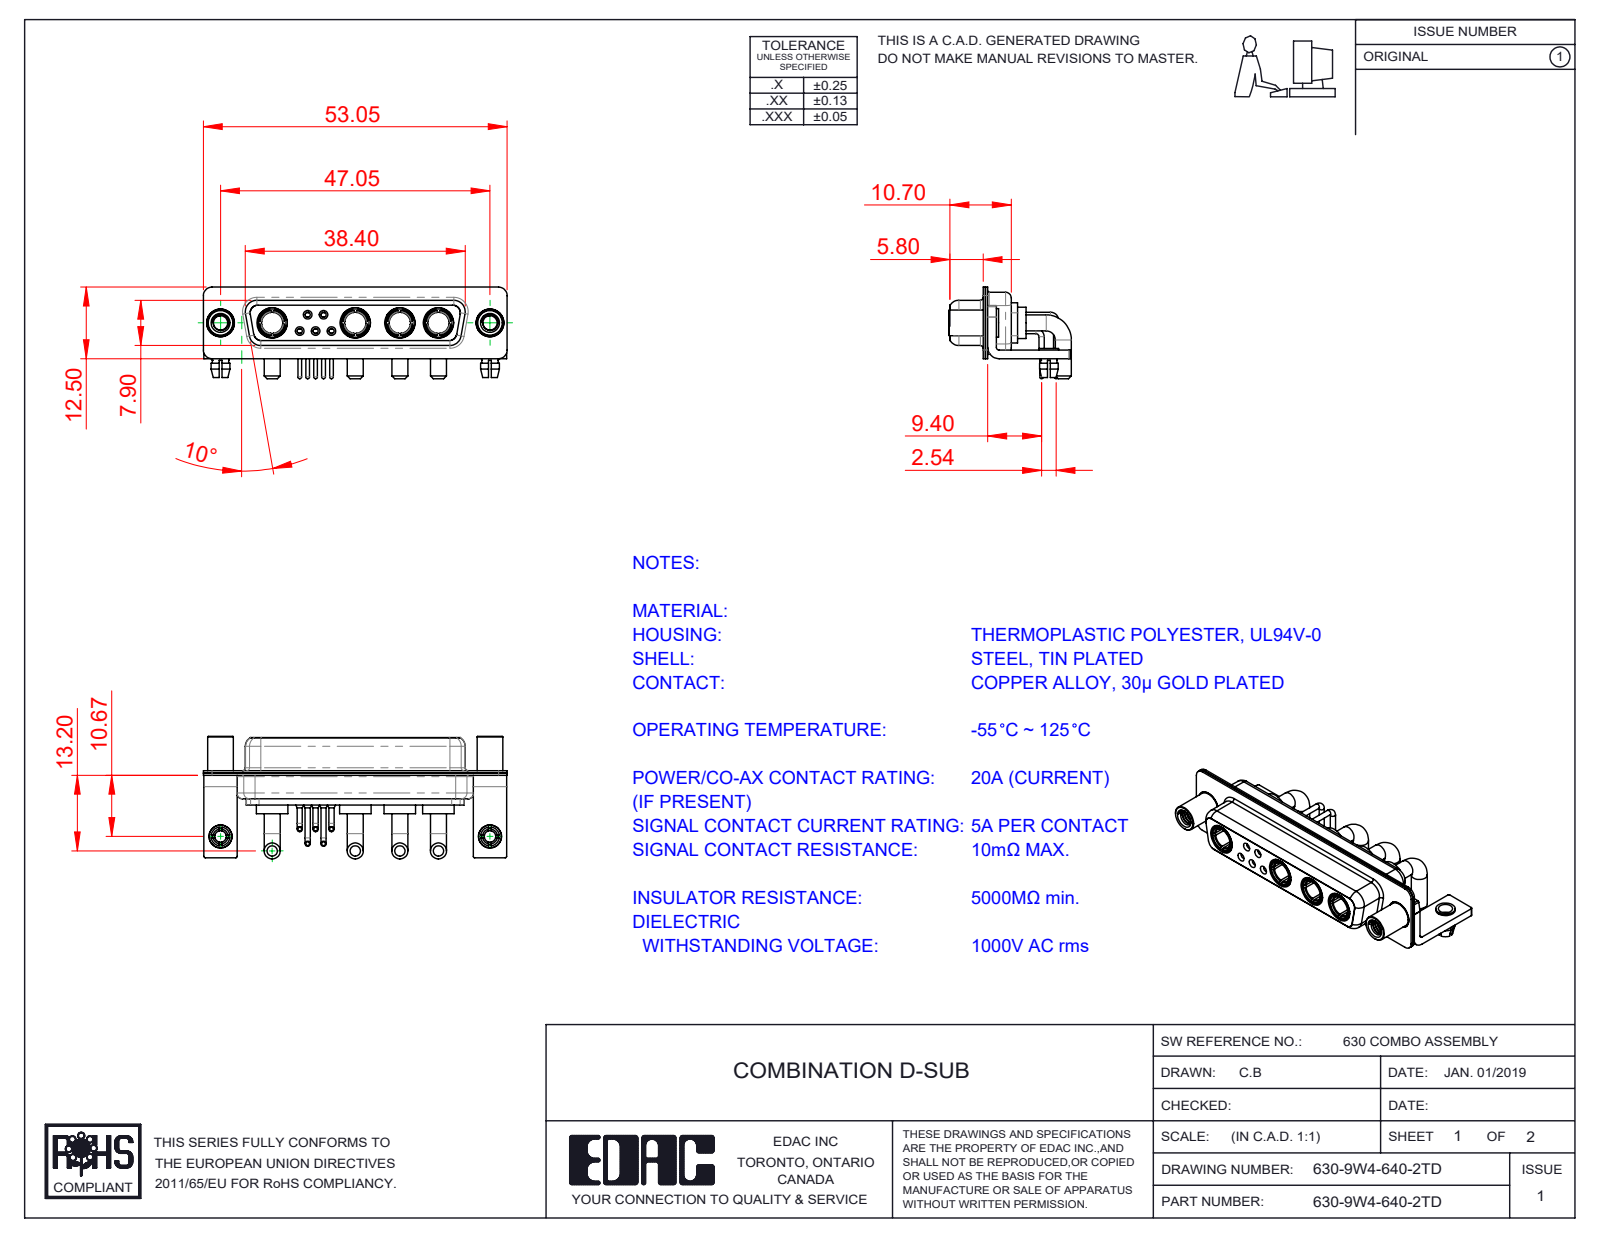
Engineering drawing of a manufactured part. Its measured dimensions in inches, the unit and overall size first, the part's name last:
Units: inches
Overall size (bounding box): 2.089 × 0.843 × 0.63
Round holes (diameter × count): ⌀0.079 ×7, ⌀0.191 ×6, ⌀0.035 ×5, ⌀0.043 ×5, ⌀0.059 ×5, ⌀0.098 ×4, ⌀0.146 ×4, ⌀0.209 ×4, ⌀0.063 ×3, ⌀0.067 ×2, ⌀0.126 ×2, ⌀0.157 ×2
Round bosses / shafts (diameter × count): ⌀0.11 ×8, ⌀0.035 ×5, ⌀0.026 ×5, ⌀0.217 ×4, ⌀0.205 ×4, ⌀0.195 ×4, ⌀0.187 ×4, ⌀0.148 ×4
Partial cylindrical surfaces — rounded edges, fillets, slot ends (radius × count): R0.01 ×16, R0.059 ×16, R0.079 ×13, R0.053 ×8, R0.063 ×8, R0.02 ×5, R0.024 ×4, R0.026 ×4
Main face-to-face distances: 0.016, 0.018, 0.055, 0.333, 0.071, 0.031, 0.35, 0.059, 0.278, 0.244
Hole centre spacings: 0.124, 0.109, 1.852, 0.173, 0.198, 0.198, 0.198, 0.218
Volume: 0.271 in³ · Surface area: 15.47 in²
Bodies: 22 solids, 1046 faces (328 planar, 456 cylindrical, 262 other)
Part name (STEP PRODUCT): 630Combo Shell Front_25 Contacts; 630Combo Contact Row 1; 630Combo Threaded Standoff_D; 630Combo Board Lock (+6 more)
STEP written by: SolidWorks 2020 (CONFIG_CONTROL_DESIGN)
